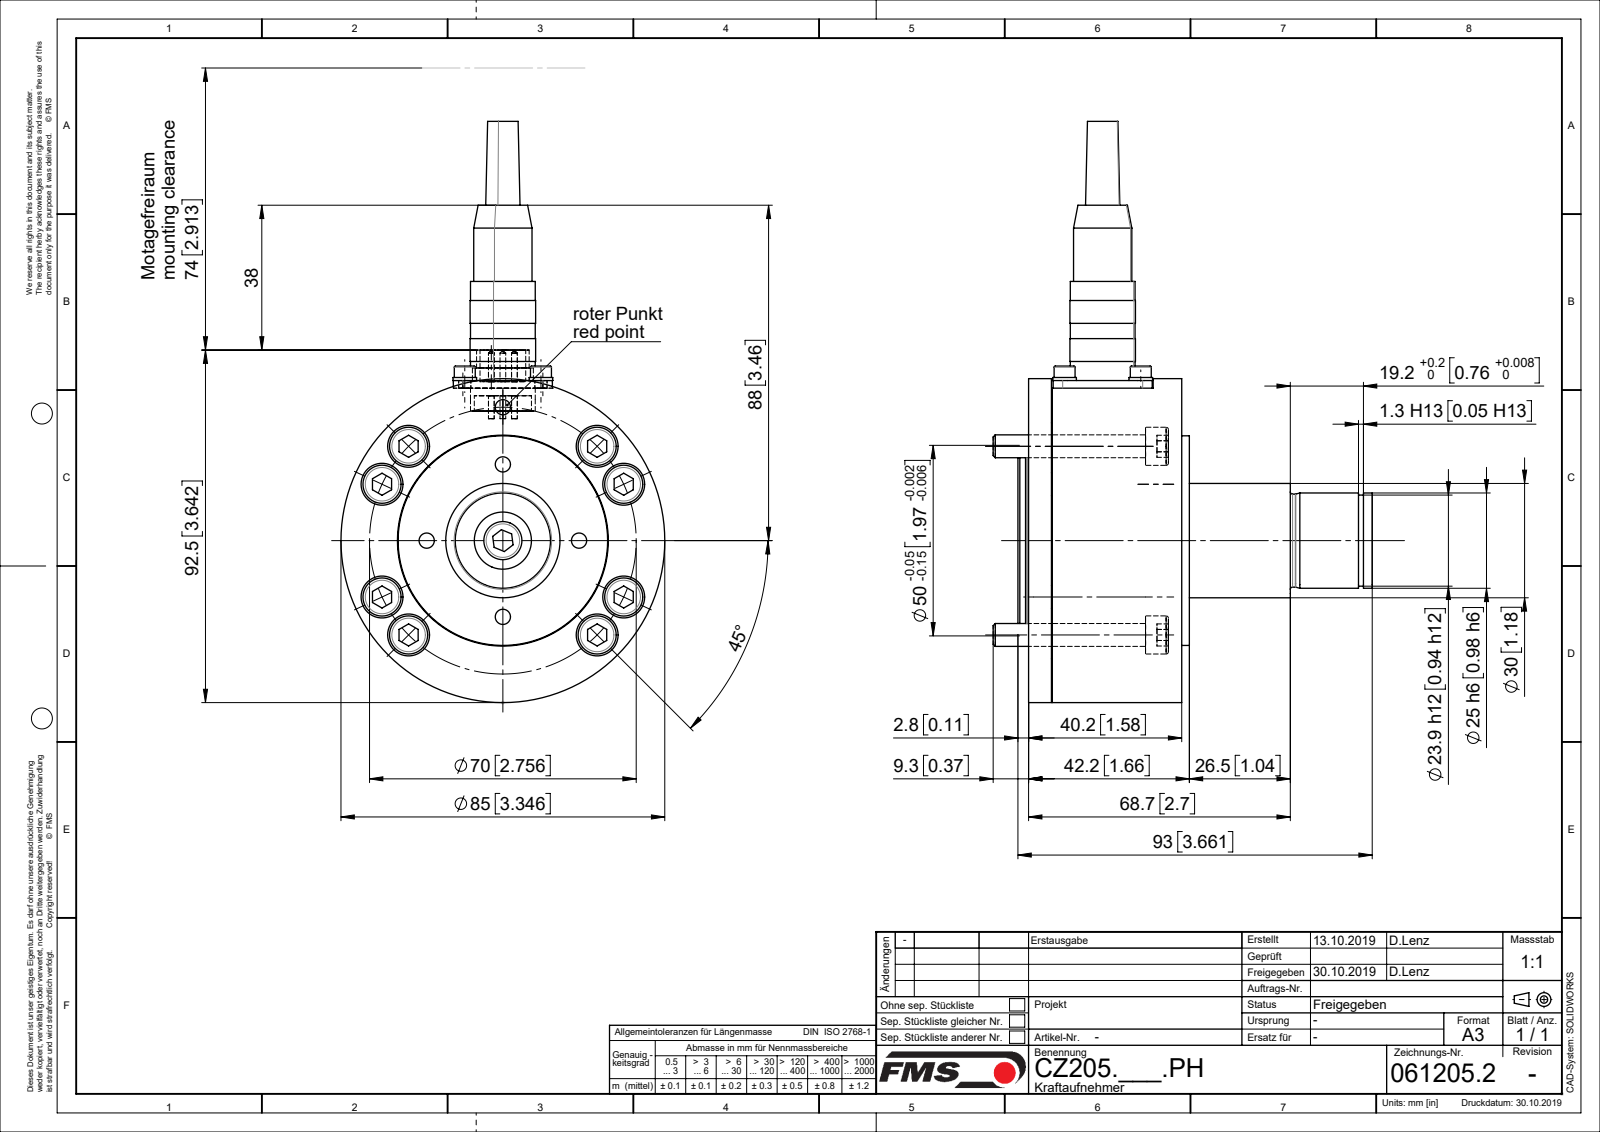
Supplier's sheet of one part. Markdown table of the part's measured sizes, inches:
| quantity | value |
| --- | --- |
| part name | ZEICHNUNG3; C0612052; C0709081; C0612056 (+8 more) |
| STEP written by | Mechanical Desktop 2009 (CONFIG_CONTROL_DESIGN) |
| units | inches |
| bodies | 27 solids, 538 faces (189 planar, 251 cylindrical, 98 other) |
| overall size | 6.004 × 3.917 × 3.346 |
| volume | 13.68 in³ |
| surface area | 127.3 in² |
| round holes (diameter × count) | 0.256 × 8, 0.433 × 8, 0.102 × 4, 0.126 × 4, 0.157 × 4, 0.203 × 4, 0.276 × 4, 0.591 × 2, 0.281 × 1, 0.354 × 1, 0.42 × 1, 0.472 × 1 |
| round bosses / shafts (diameter × count) | 0.394 × 8, 0.236 × 8, 0.059 × 5, 0.244 × 4, 0.217 × 4, 0.197 × 4, 0.118 × 4, 3.346 × 1 |
| partial cylindrical surfaces (radius × count) | 0.098 × 4, 0.197 × 2 |
| main face-to-face distances | 0.236, 0.079, 0.118, 1.575, 1.654, 1.339, 1.319, 1.772, 1.417, 0.315 |
| hole center spacings | 0.787, 0.992, 1.378, 2.013, 1.113, 0.479, 0.557, 0.743 |
